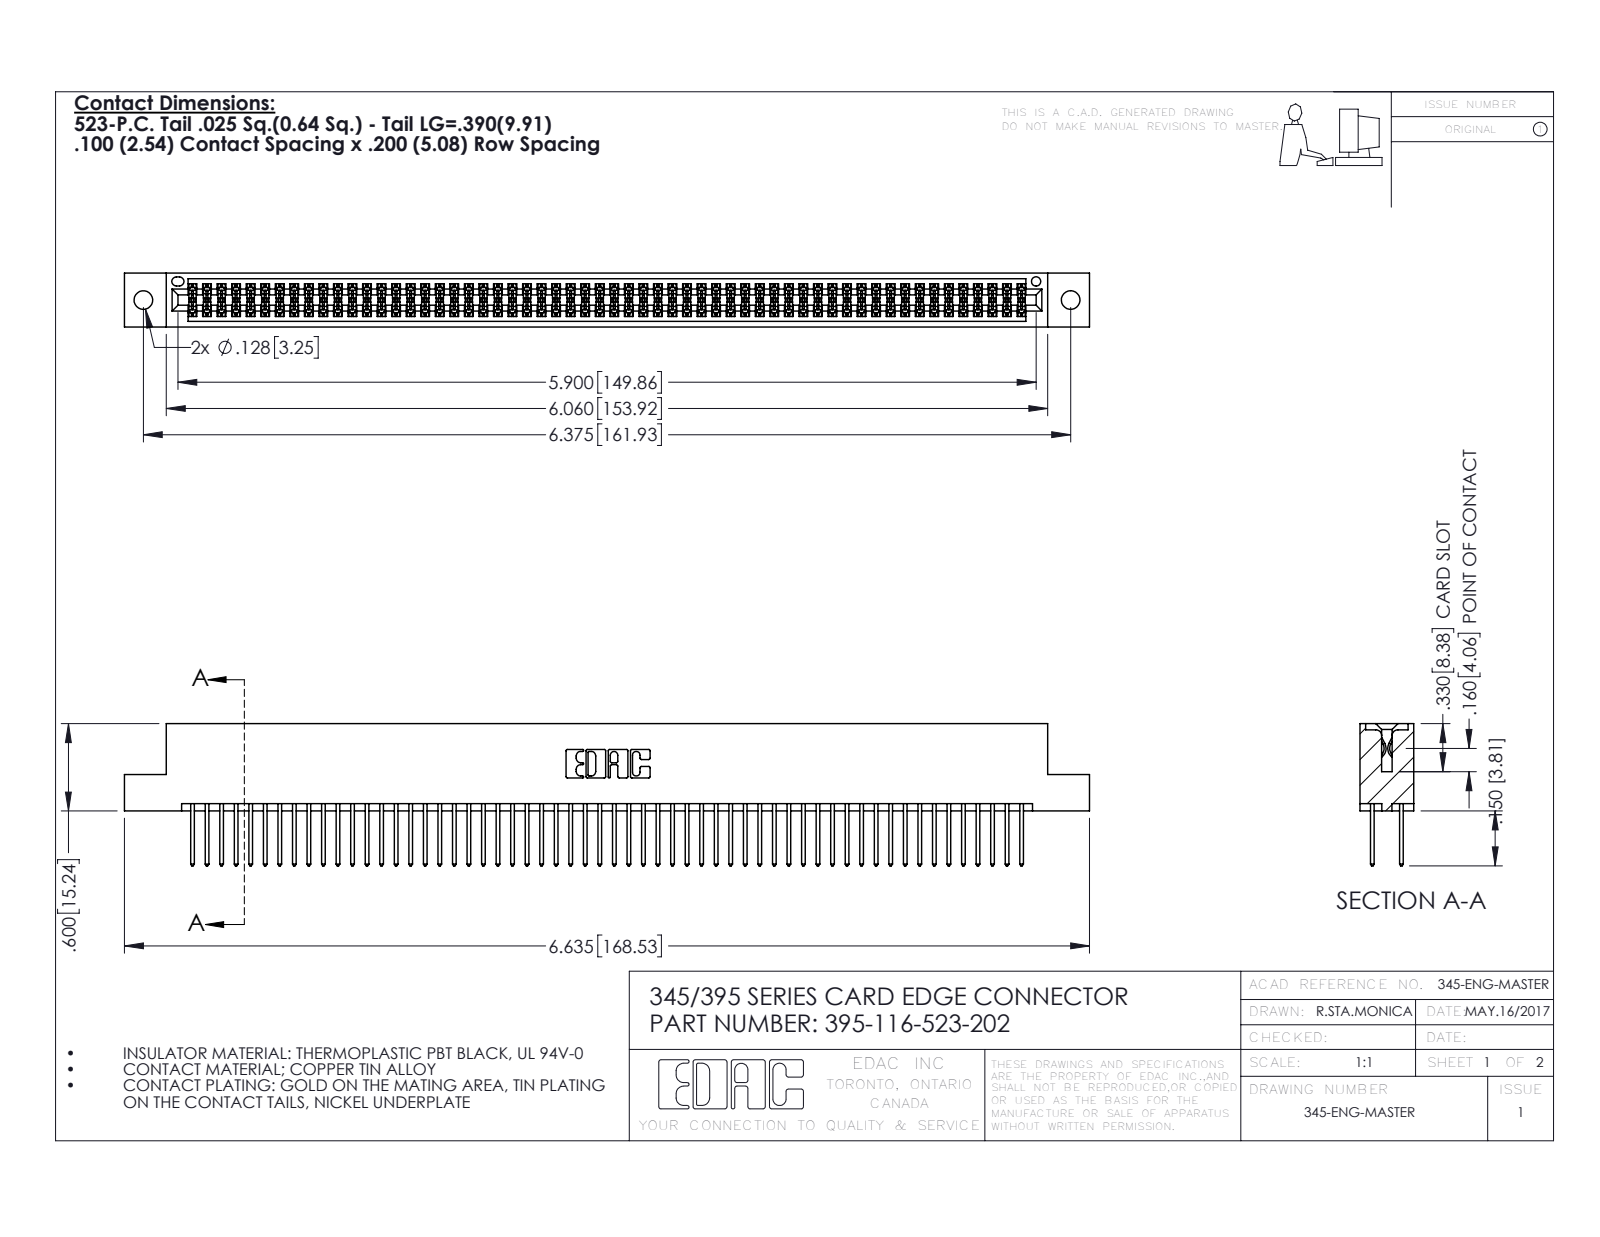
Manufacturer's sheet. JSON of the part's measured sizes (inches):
{"part_name": "395-116-523-202; 345 Part_Flush Mounting Lugs - 0.128 Dia; 345-292-001_345-293-123", "step_written_by": "SolidWorks 2016 (CONFIG_CONTROL_DESIGN)", "units": "inches", "bodies": {"solids": 117, "faces": 5926, "planar": 3908, "cylindrical": 2018, "other": 0}, "overall_size": [6.635, 0.977, 0.37], "volume_in3": 1.02, "surface_area_in2": 40.02, "round_holes": [[0.128, 2], [0.064, 1]], "partial_cylinders_radius": [[0.006, 174], [0.01, 116], [0.01, 22], [0.007, 6], [0.031, 6], [0.026, 3], [0.014, 2], [0.019, 2]], "face_to_face_distances": [0.298, 0.072, 0.2, 0.098, 0.272, 0.025, 0.37, 0.225, 0.175, 0.149], "hole_center_spacings": [0.27, 6.139, 6.375]}
